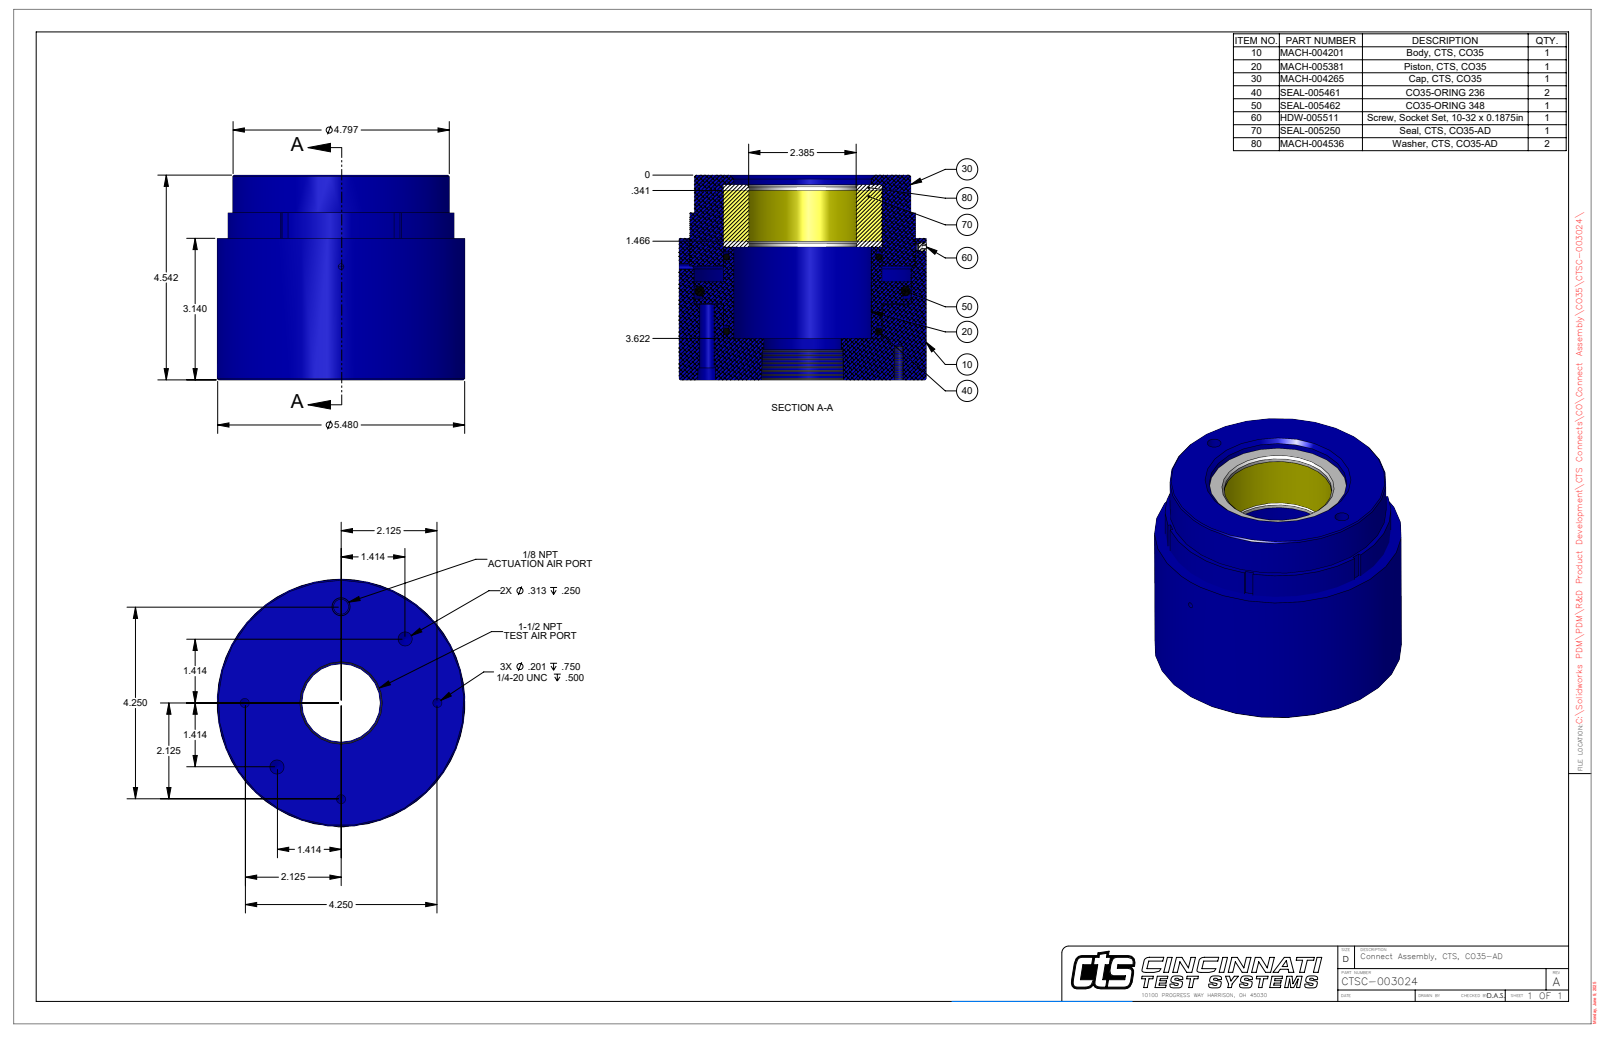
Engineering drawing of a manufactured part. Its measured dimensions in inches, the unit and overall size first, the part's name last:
Units: inches
Overall size (bounding box): 5.486 × 5.48 × 4.542
Round holes (diameter × count): ⌀0.313 ×4, ⌀0.201 ×3, ⌀0.125 ×1, ⌀0.332 ×1, ⌀1.719 ×1, ⌀2.385 ×1, ⌀2.387 ×1, ⌀3.05 ×1, ⌀3.517 ×1
Round bosses / shafts (diameter × count): ⌀5.48 ×1, ⌀5 ×1, ⌀4.797 ×1, ⌀3.513 ×1, ⌀3.509 ×1
Partial cylindrical surfaces — rounded edges, fillets, slot ends (radius × count): R2.46 ×1, R2.73 ×1
Main face-to-face distances: 4.201, 4.542, 0.341, 0.125, 4.326, 0.216, 0.92, 3.281, 3.406, 3.622
Hole centre spacings: 1.583, 2, 2.125, 2.918, 3.005, 3.811, 0.125, 1.531
Volume: 75.09 in³ · Surface area: 181.8 in²
Bodies: 2 solids, 129 faces (49 planar, 56 cylindrical, 24 other)
Part name (STEP PRODUCT): CTSC-003024
STEP written by: SolidWorks 2023 (AUTOMOTIVE_DESIGN)
